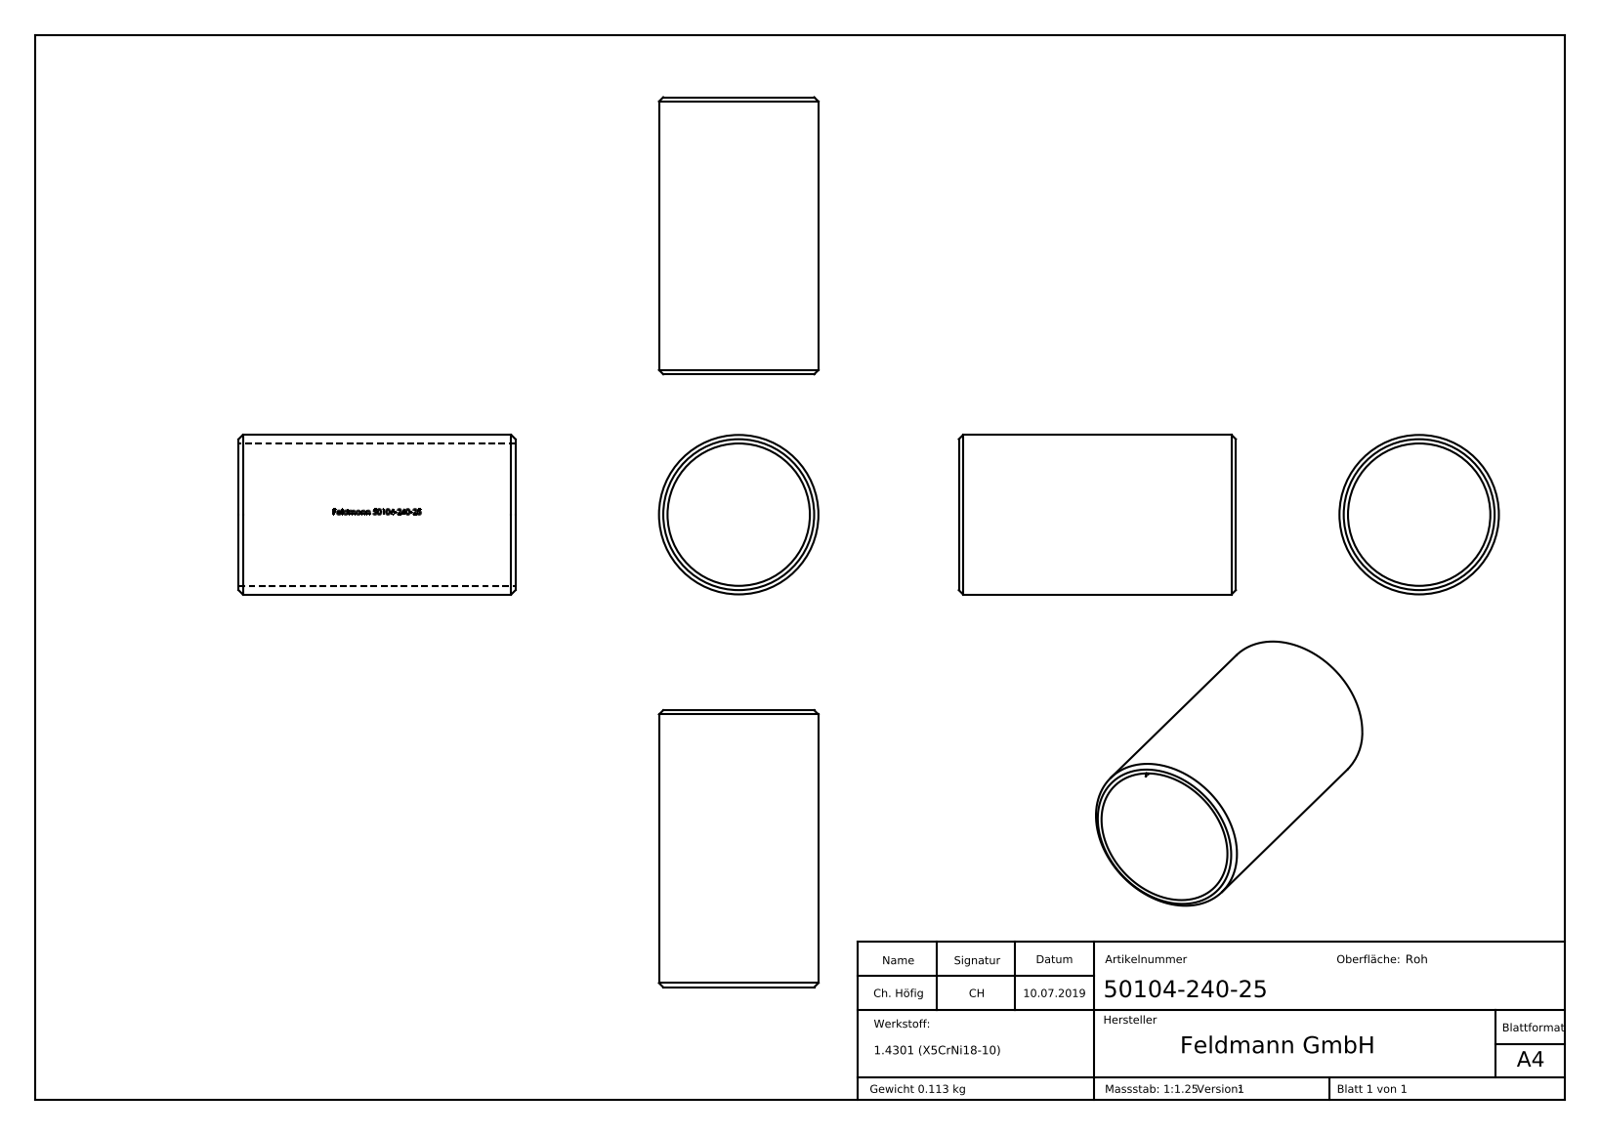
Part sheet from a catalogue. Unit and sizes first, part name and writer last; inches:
Units: inches
Overall size (bounding box): 2.559 × 1.472 × 1.472
Round holes (diameter × count): ⌀1.315 ×1
Round bosses / shafts (diameter × count): ⌀1.472 ×1
Partial cylindrical surfaces — rounded edges, fillets, slot ends (radius × count): R0.661 ×1
Main face-to-face distances: 2.559, 0.017, 0.035, 0.383, 0.052, 0.08, 0.023, 0.462, 0.084, 0.467
Volume: 0.875 in³ · Surface area: 22.9 in²
Bodies: 1 solid, 273 faces (120 planar, 46 cylindrical, 107 other)
Part name (STEP PRODUCT): 50104-240-25
STEP written by: SolidWorks 2015 (CONFIG_CONTROL_DESIGN)
